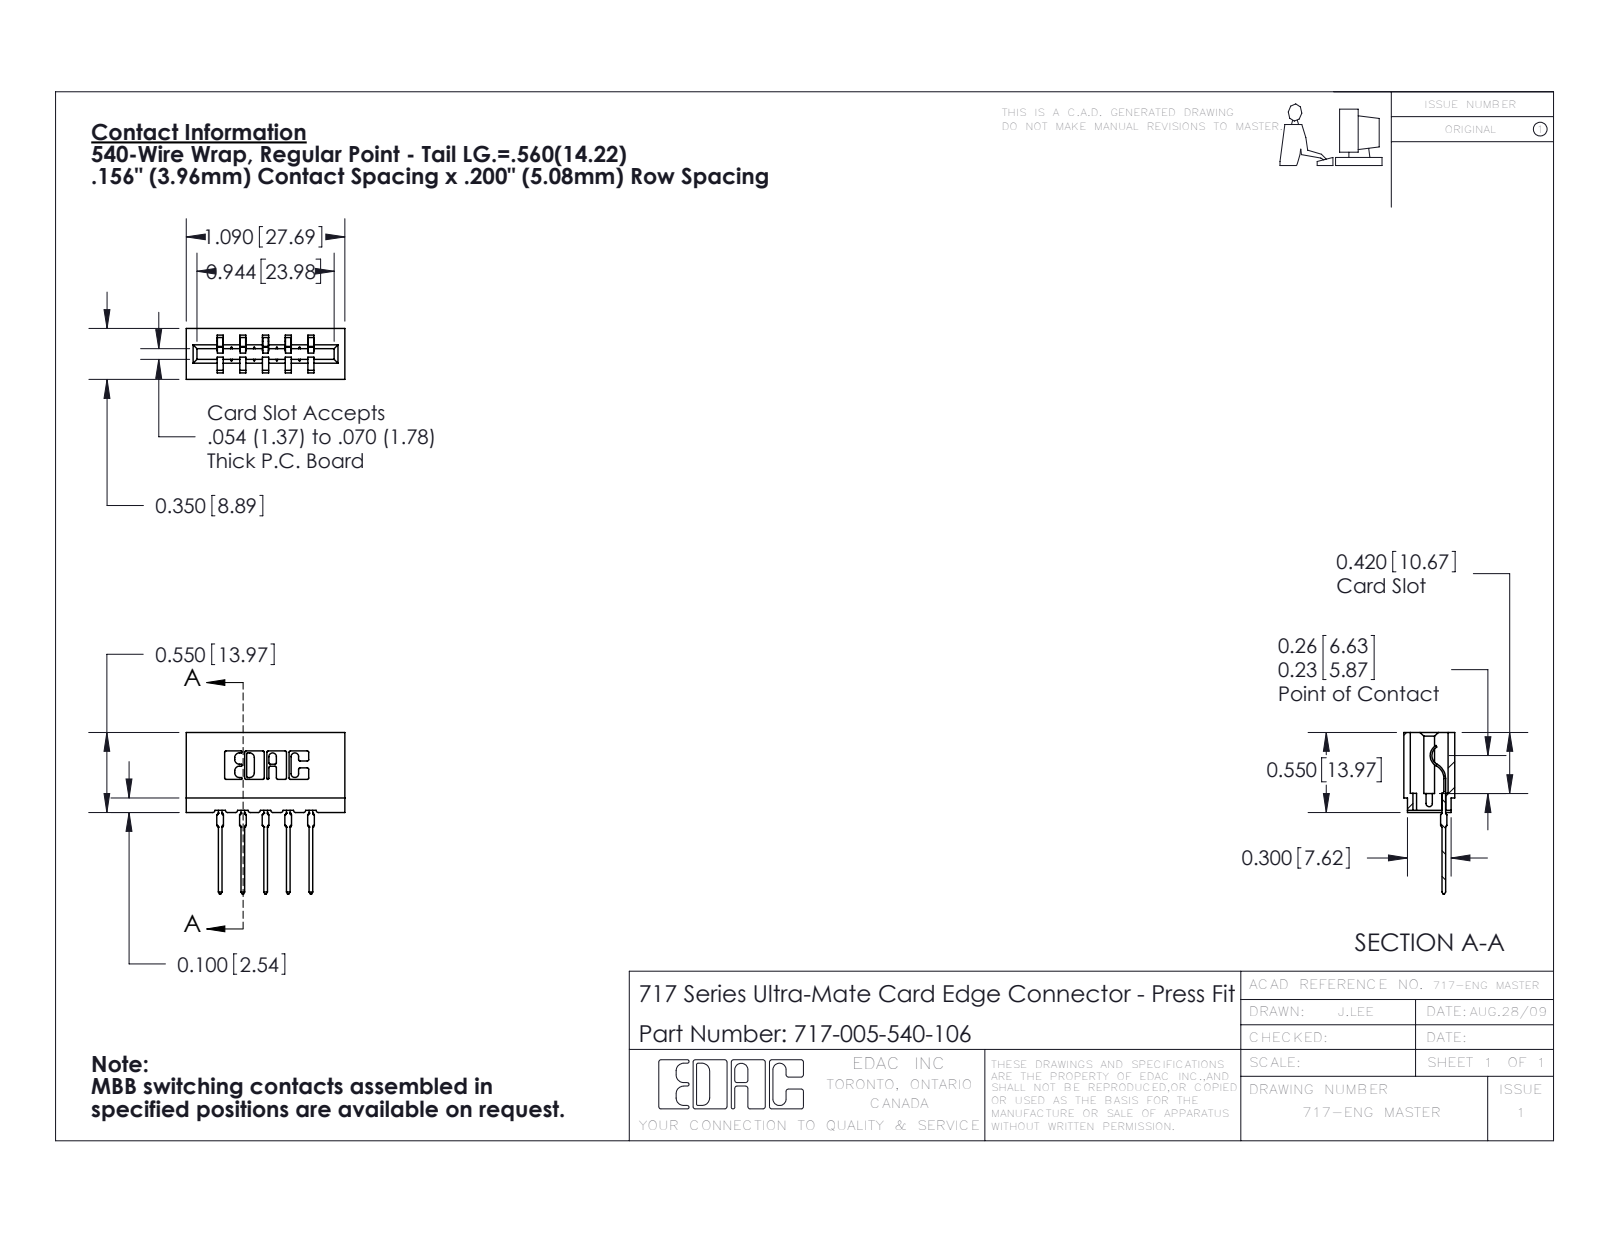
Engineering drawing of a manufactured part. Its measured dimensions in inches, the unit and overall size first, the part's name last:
Units: inches
Overall size (bounding box): 1.109 × 1.09 × 0.35
Partial cylindrical surfaces — rounded edges, fillets, slot ends (radius × count): R0.01 ×22, R0.015 ×10, R0.021 ×10, R0.007 ×6, R0.031 ×6, R0.005 ×4, R0.011 ×4, R0.026 ×3
Main face-to-face distances: 0.212, 0.156, 0.138, 0.35, 0.198, 0.042, 0.312, 0.468, 0.312, 0.074
Volume: 0.154 in³ · Surface area: 4.947 in²
Bodies: 6 solids, 659 faces (394 planar, 135 cylindrical, 130 other)
Part name (STEP PRODUCT): 745-292-001_540; 717 Part_Insulator Option - 06; 717-005-540-106
STEP written by: SolidWorks 2016 (CONFIG_CONTROL_DESIGN)
